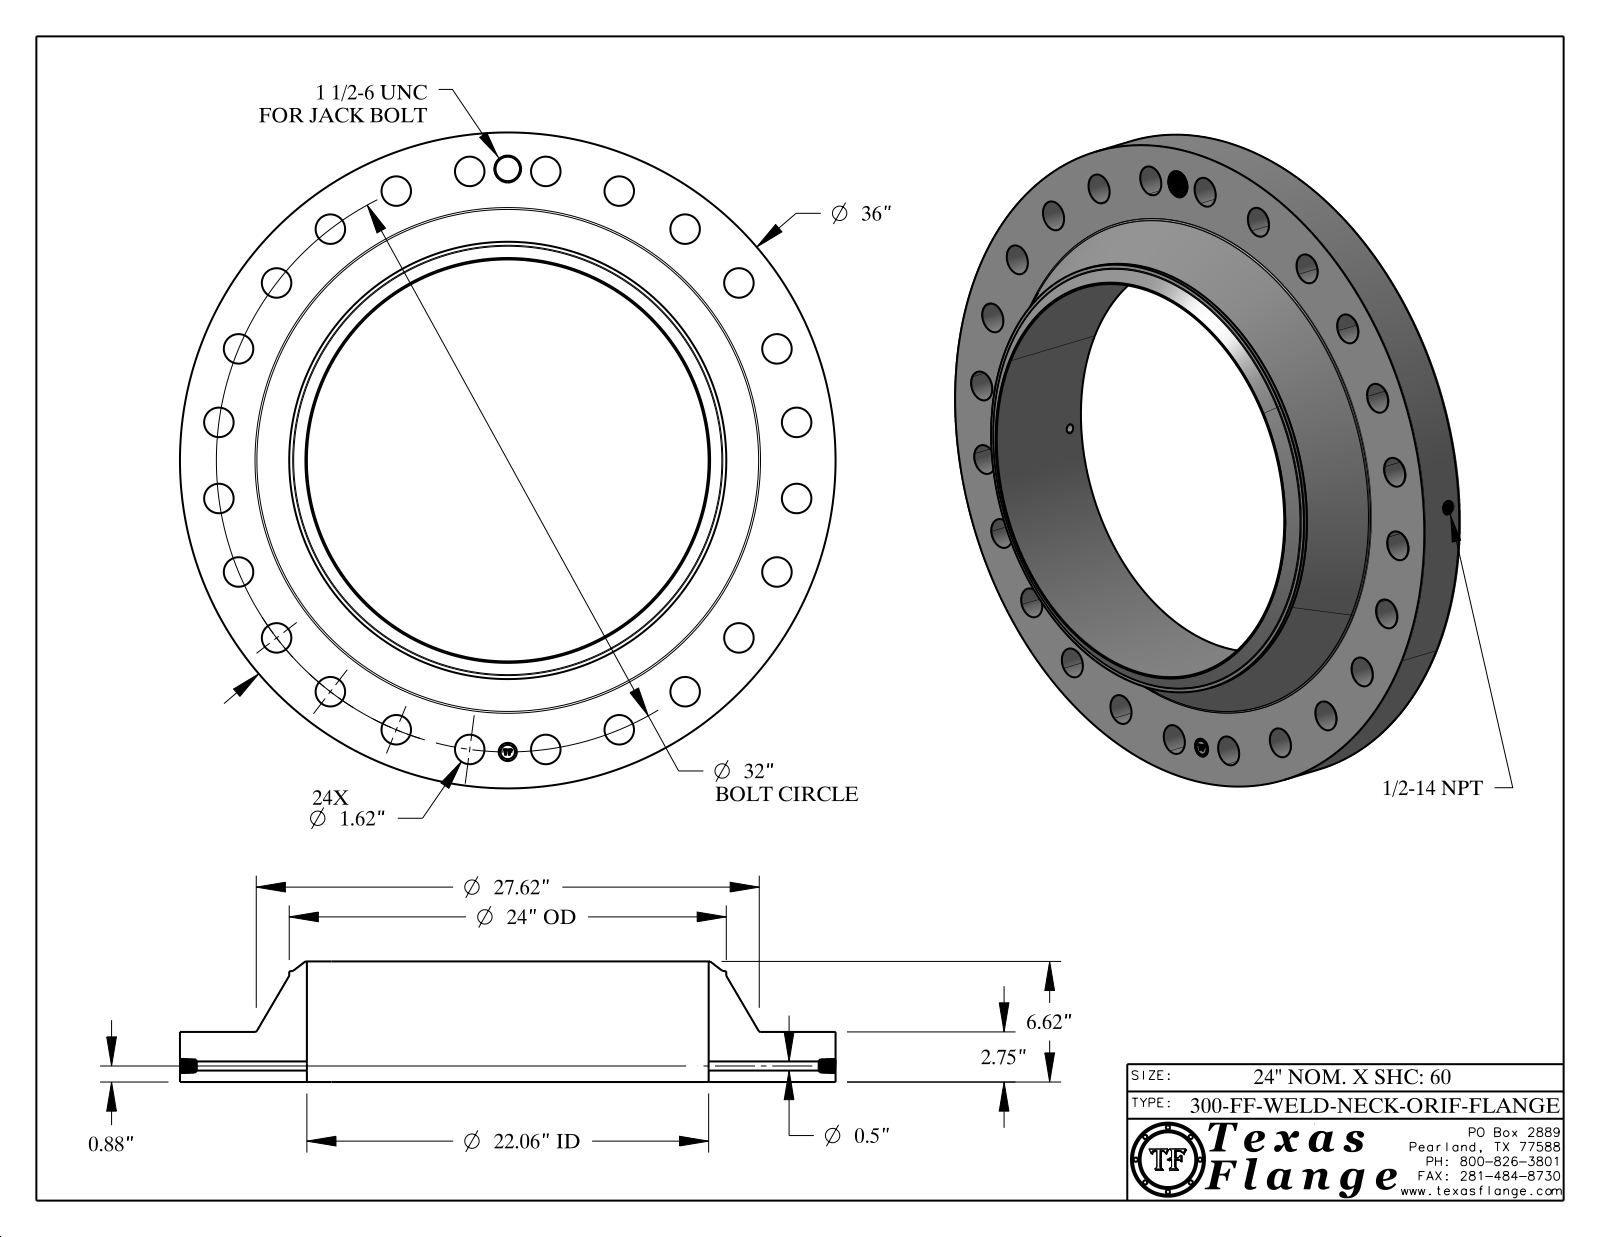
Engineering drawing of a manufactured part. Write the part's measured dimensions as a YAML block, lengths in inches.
part_name: "300-FF-WELD-NECK"
step_written_by: "CATIA V5 STEP AP214 (AUTOMOTIVE_DESIGN)"
units: inches
bodies: {solids: 1, faces: 811, planar: 368, cylindrical: 127, other: 316}
overall_size: [36, 36, 6.62]
volume: 2075
surface_area: 2489
round_holes:
  - {diameter: 1.62, count: 24}
  - {diameter: 0.5, count: 1}
  - {diameter: 0.672, count: 1}
  - {diameter: 1, count: 1}
  - {diameter: 1.344, count: 1}
  - {diameter: 22.062, count: 1}
round_bosses_or_shafts:
  - {diameter: 0.061, count: 8}
  - {diameter: 36, count: 1}
  - {diameter: 24, count: 1}
  - {diameter: 0.788, count: 1}
face_to_face_distances: [2.75, 6.62, 3.87, 2.735, 0.015, 3.885, 0.298, 0.293, 0.054, 0.248]
hole_center_spacings: [16, 27.713, 30.909, 4.177, 19.48, 31.726, 8.282, 12.246]
